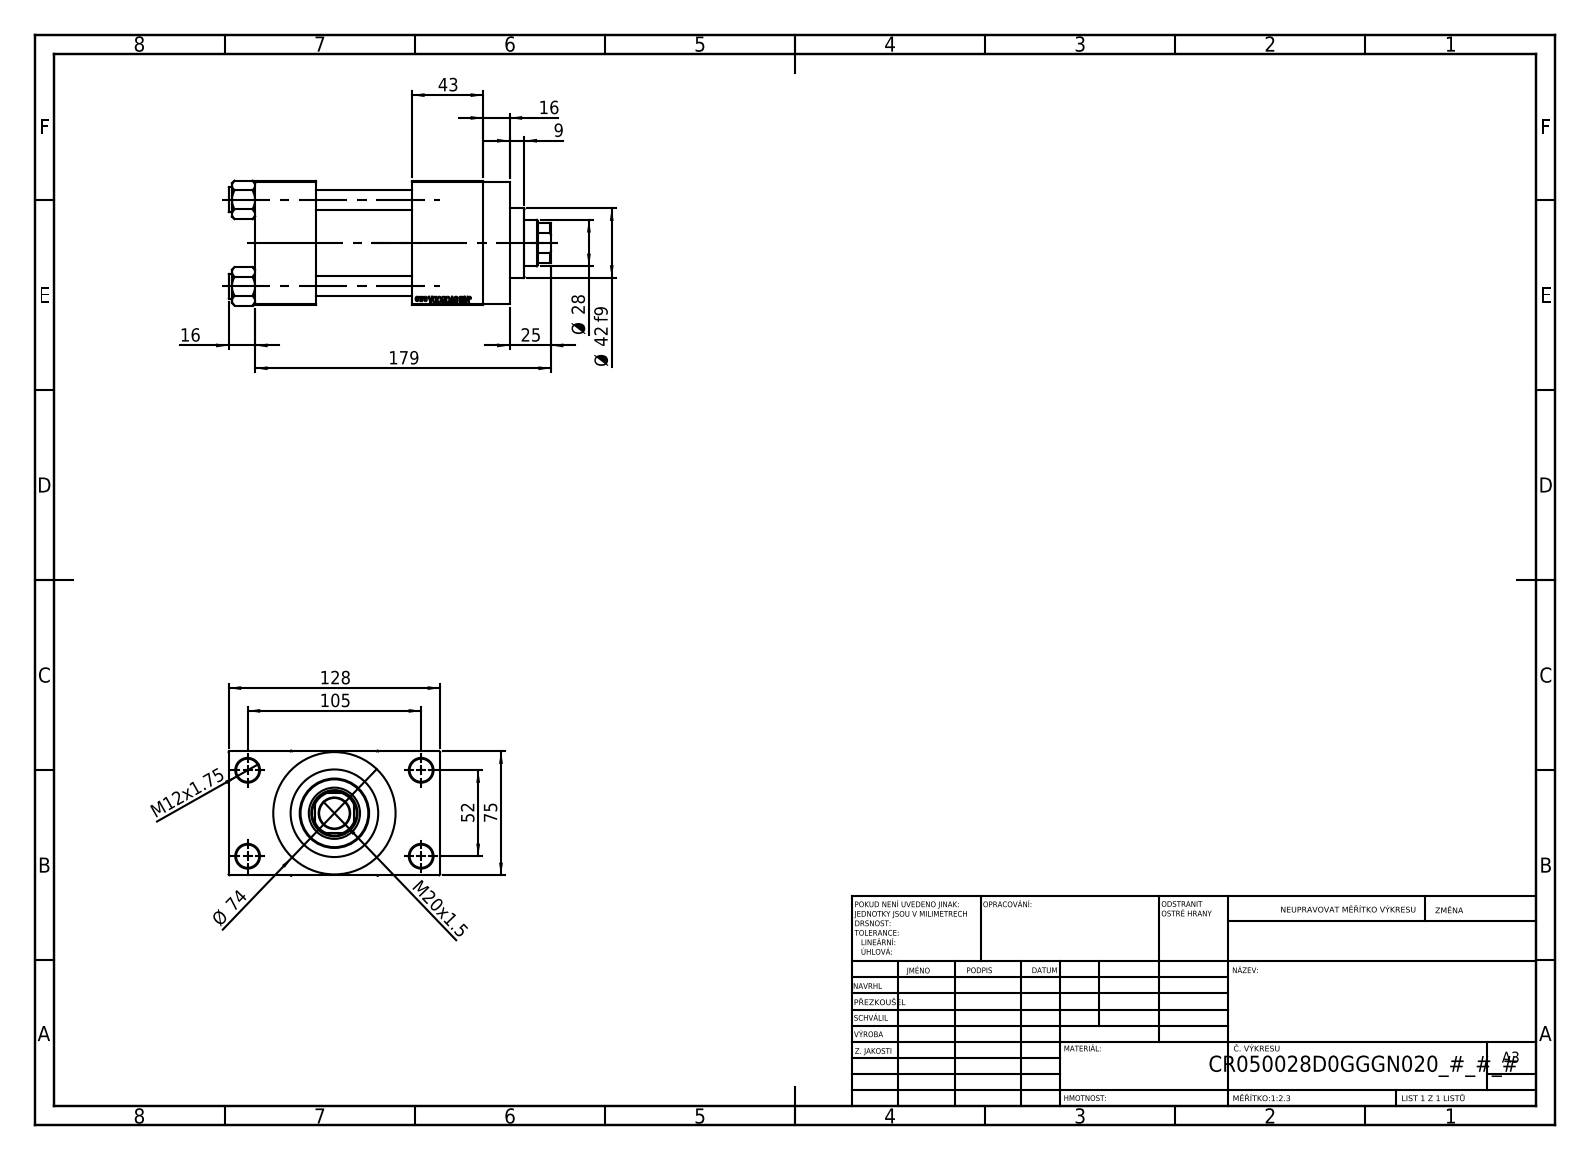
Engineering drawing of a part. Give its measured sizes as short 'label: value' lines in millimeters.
name: NUT_M5_D; V215CR_D_Body; V215CR_VCP_D; V215CR_D_TYCINKA (+1 more)
written by: SolidWorks 2019 (CONFIG_CONTROL_DESIGN)
unit: mm
bodies: 11 solids, 1104 faces (497 planar, 89 cylindrical, 518 other)
size: 195 × 128 × 75.54
volume: 815 231 mm³; area: 168 868 mm²
holes: 4× ⌀12, 4× ⌀14, 2× ⌀7, 2× ⌀20.96, 2× ⌀30, 1× ⌀18.5, 1× ⌀28, 1× ⌀31, 1× ⌀41, 1× ⌀50, 1× ⌀53
bosses: 4× ⌀15, 1× ⌀74, 1× ⌀56, 1× ⌀42
rounds: 1× R13.5
face distances: 75, 58, 37, 95, 26.5, 101.5, 138, 101, 43, 16
hole spacings: 26.35, 36.98, 52.3, 58.43, 58.59, 78.65, 94.37, 52
